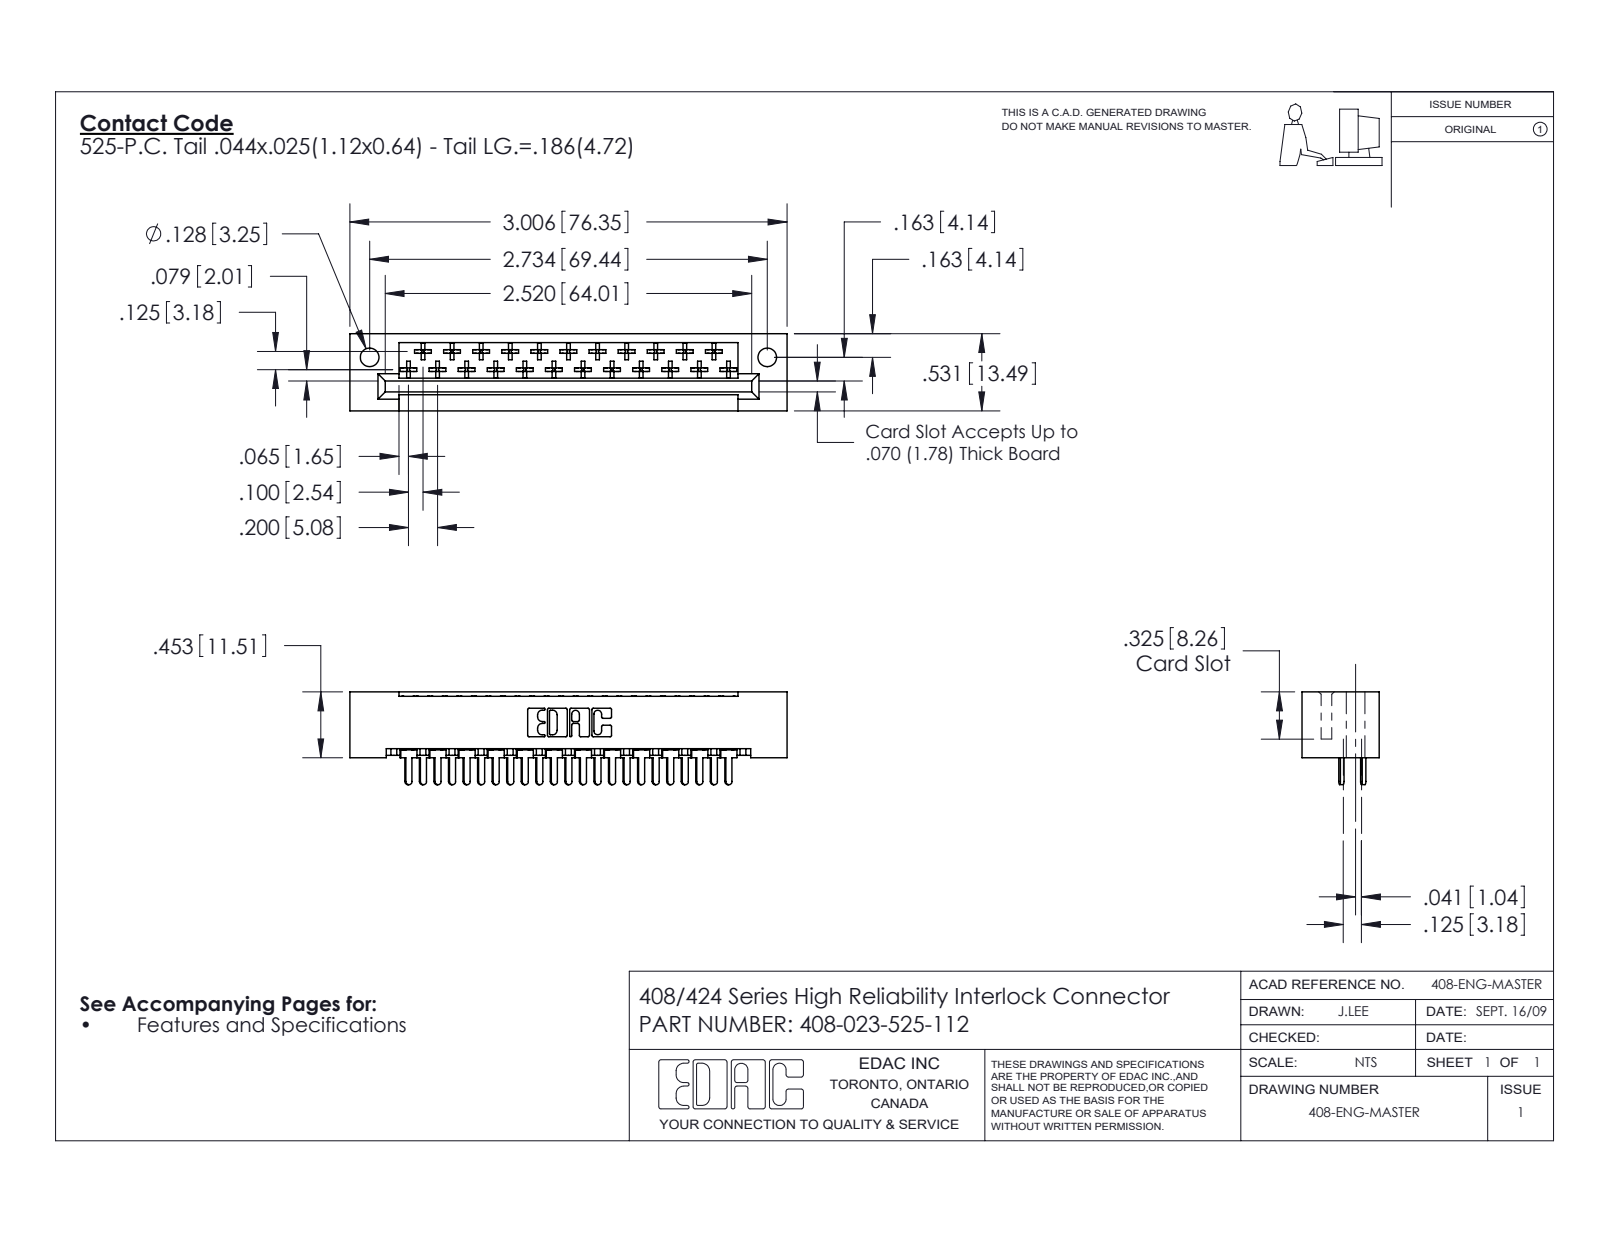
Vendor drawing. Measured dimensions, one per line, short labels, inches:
name: 408-290-001_408-290-125 - Bottom; 408-023-525-112; 408 Part_023 - 1; 408-290-001_408-290-125 - Top
written by: SolidWorks 2016 (CONFIG_CONTROL_DESIGN)
unit: in
bodies: 24 solids, 1392 faces (1045 planar, 255 cylindrical, 92 other)
size: 3.006 × 0.638 × 0.531
volume: 0.541 in³; area: 15.77 in²
holes: 2× ⌀0.128
rounds: 138× R0.01, 25× R0.02, 23× R0.022, 22× R0.01, 6× R0.007, 6× R0.031, 3× R0.026
face distances: 0.531, 0.4, 0.025, 0.1, 0.125, 0.025, 0.272, 0.235, 0.259, 0.296
hole spacings: 2.734
